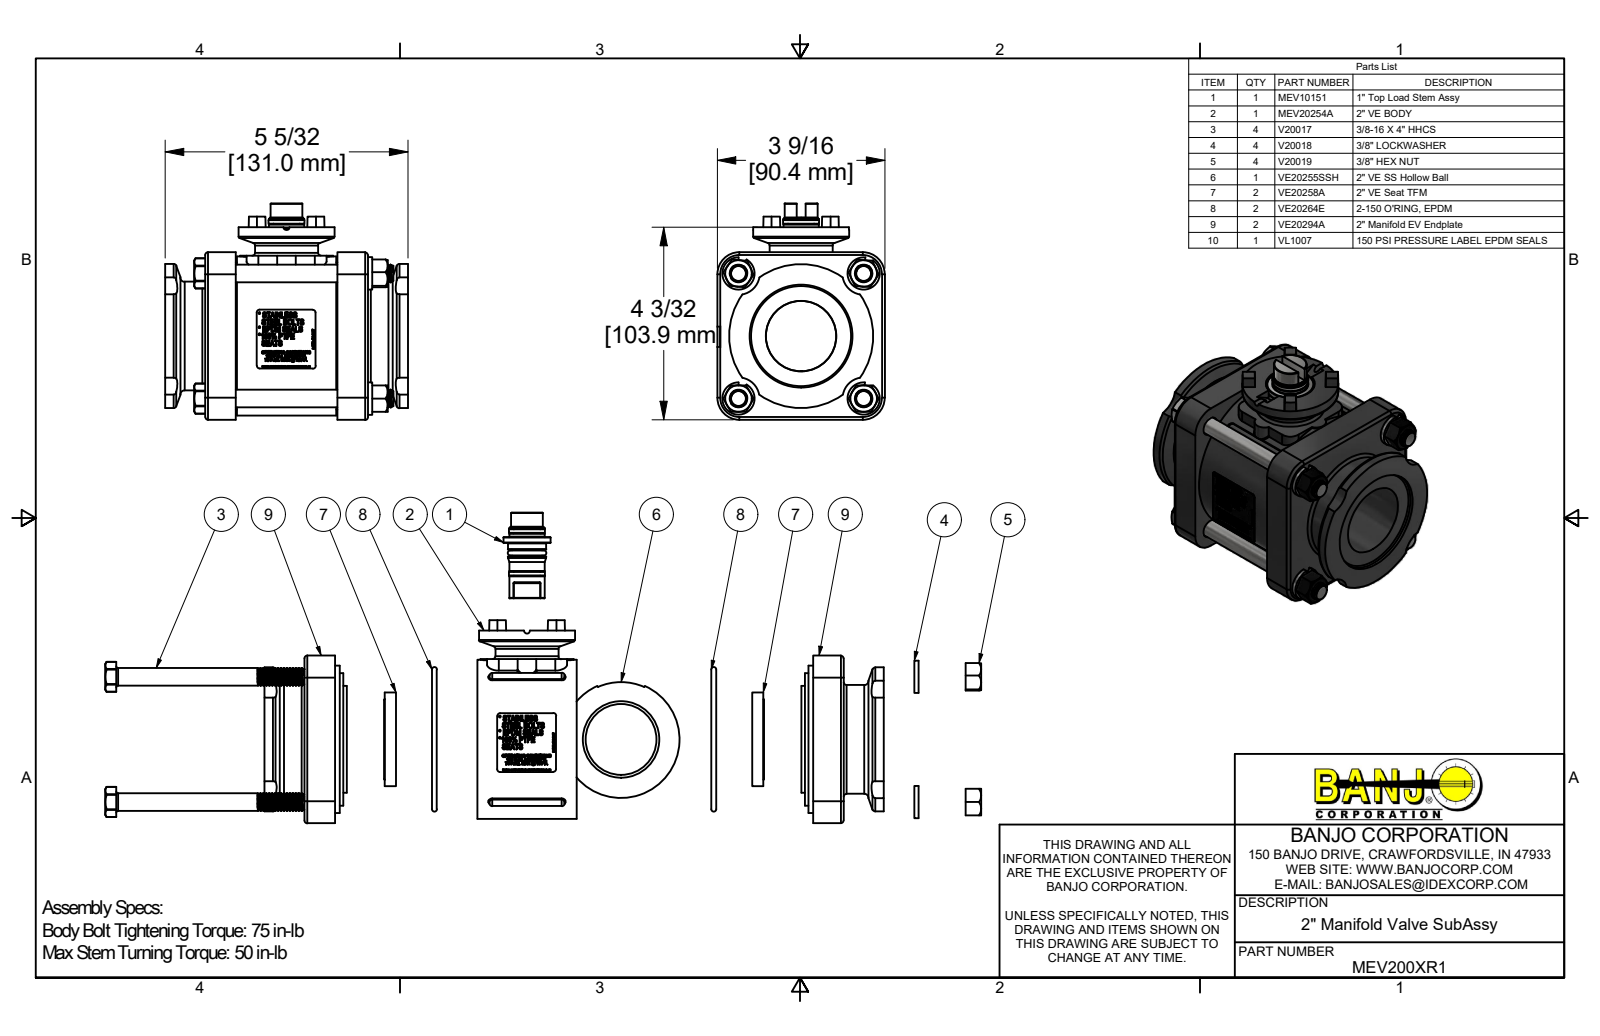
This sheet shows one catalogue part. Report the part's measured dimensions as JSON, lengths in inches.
{"part_name": "MEV200XR1; MEV20254A; MEV20254AX; VE20255SSH (+8 more)", "step_written_by": "Autodesk Inventor 2019 (AUTOMOTIVE_DESIGN)", "units": "inches", "bodies": {"solids": 27, "faces": 2799, "planar": 1323, "cylindrical": 371, "other": 1105}, "overall_size": [5.158, 4.596, 3.56], "volume_in3": 34.05, "surface_area_in2": 256.6, "round_holes": [[0.307, 4], [0.385, 4], [0.406, 4], [1.5, 2], [0.645, 1], [0.76, 1], [0.818, 1], [1.02, 1], [1.04, 1], [1.495, 1], [1.995, 1], [2.19, 1]], "round_bosses_or_shafts": [[0.324, 60], [0.687, 4], [0.375, 4], [3.38, 1], [3.13, 1], [2.812, 1], [2.31, 1], [2.27, 1]], "partial_cylinders_radius": [[0.06, 12], [0.01, 8], [0.02, 8], [0.162, 8], [0.09, 4], [0.21, 4], [0.25, 4], [0.32, 4]], "face_to_face_distances": [0.825, 0.65, 2.808, 2.633, 0.175, 1.983, 3.458, 0.85, 1.5, 1.675], "hole_center_spacings": [1.88, 2.659, 3.761]}
